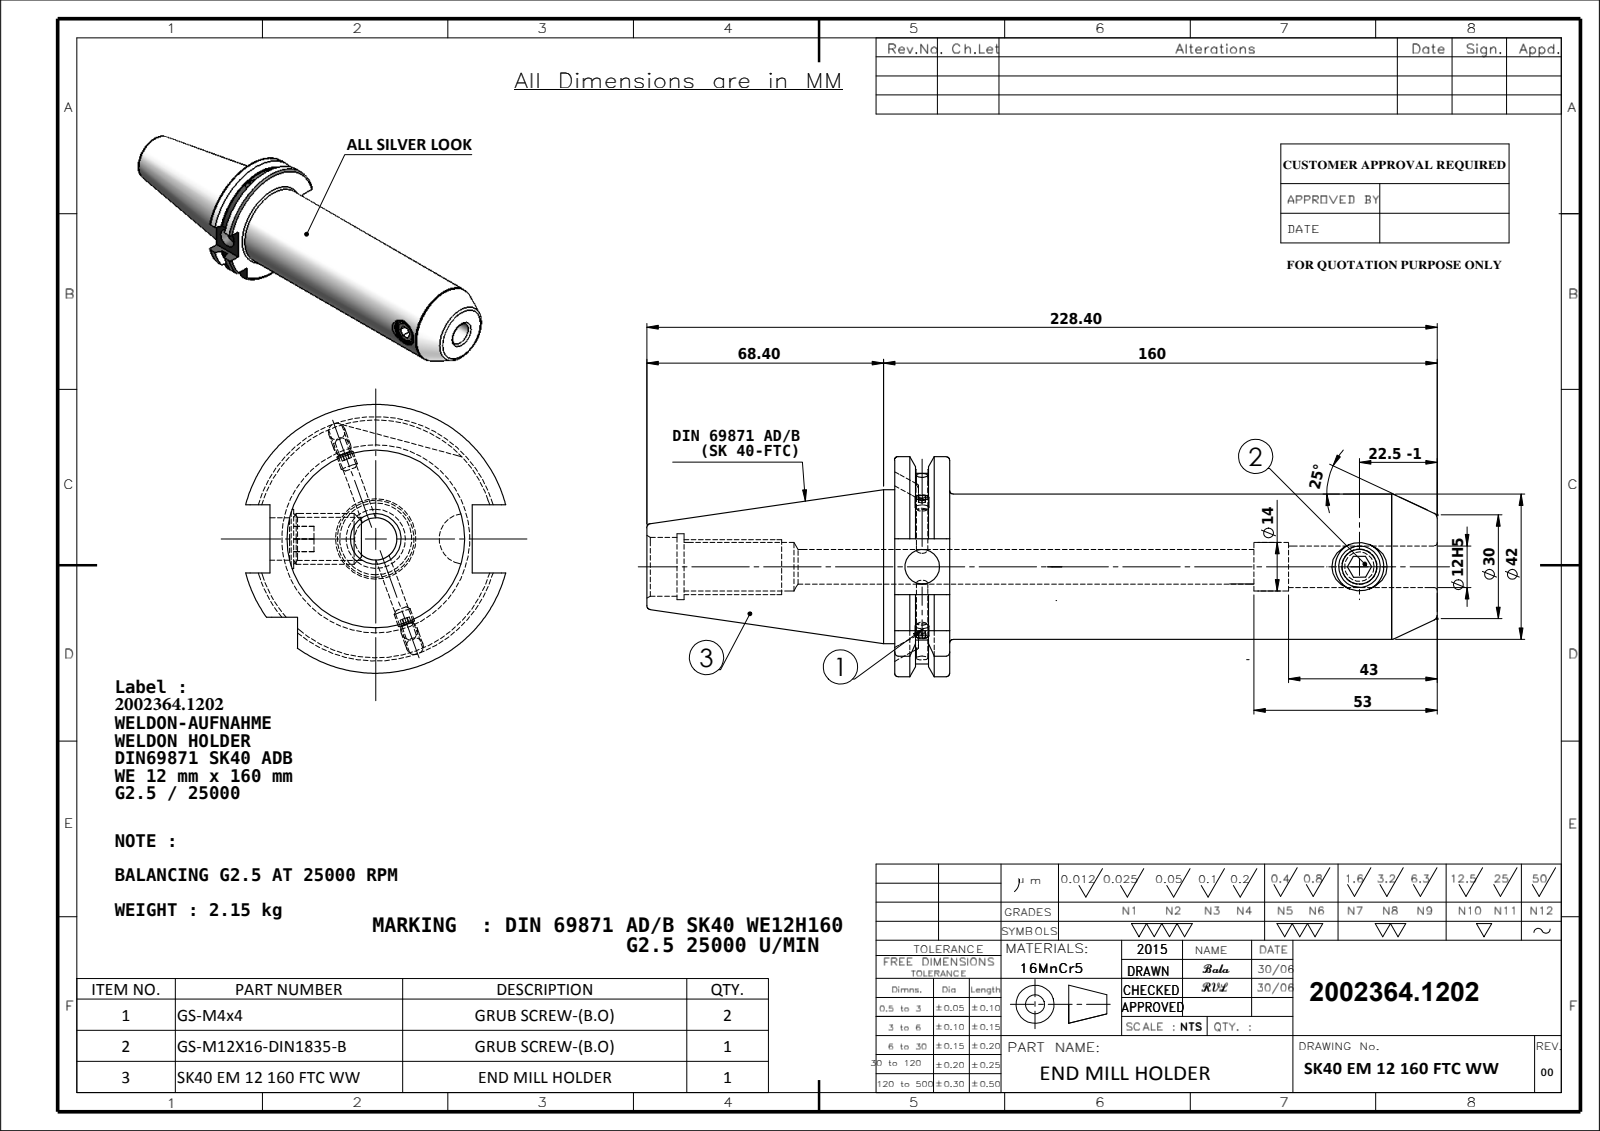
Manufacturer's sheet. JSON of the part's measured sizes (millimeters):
{"part_name": "91406-WE712160; SK40 EM 12 160 FTC WW; M12X16._ISO 4026 - M12 x 12-N; M4X4_DIN 913 - M4 x 4-N", "step_written_by": "SolidWorks 2009 (CONFIG_CONTROL_DESIGN)", "units": "millimeters", "bodies": {"solids": 5, "faces": 175, "planar": 67, "cylindrical": 46, "other": 62}, "overall_size": [228.4, 63.55, 61.48], "volume_mm3": 278931, "surface_area_mm2": 44952, "round_holes": [[10, 2], [14, 2], [3.3, 1], [10.2, 1], [12, 1], [17, 1], [19, 1]], "round_bosses_or_shafts": [[4, 2], [44.45, 1], [42, 1], [12, 1]], "partial_cylinders_radius": [[28.12, 1], [31.77, 1]], "face_to_face_distances": [15.9, 156.8, 140.9, 16.1, 47.8, 71.6, 87.5, 228.4, 10.7, 60.9], "hole_center_spacings": [126.35]}
